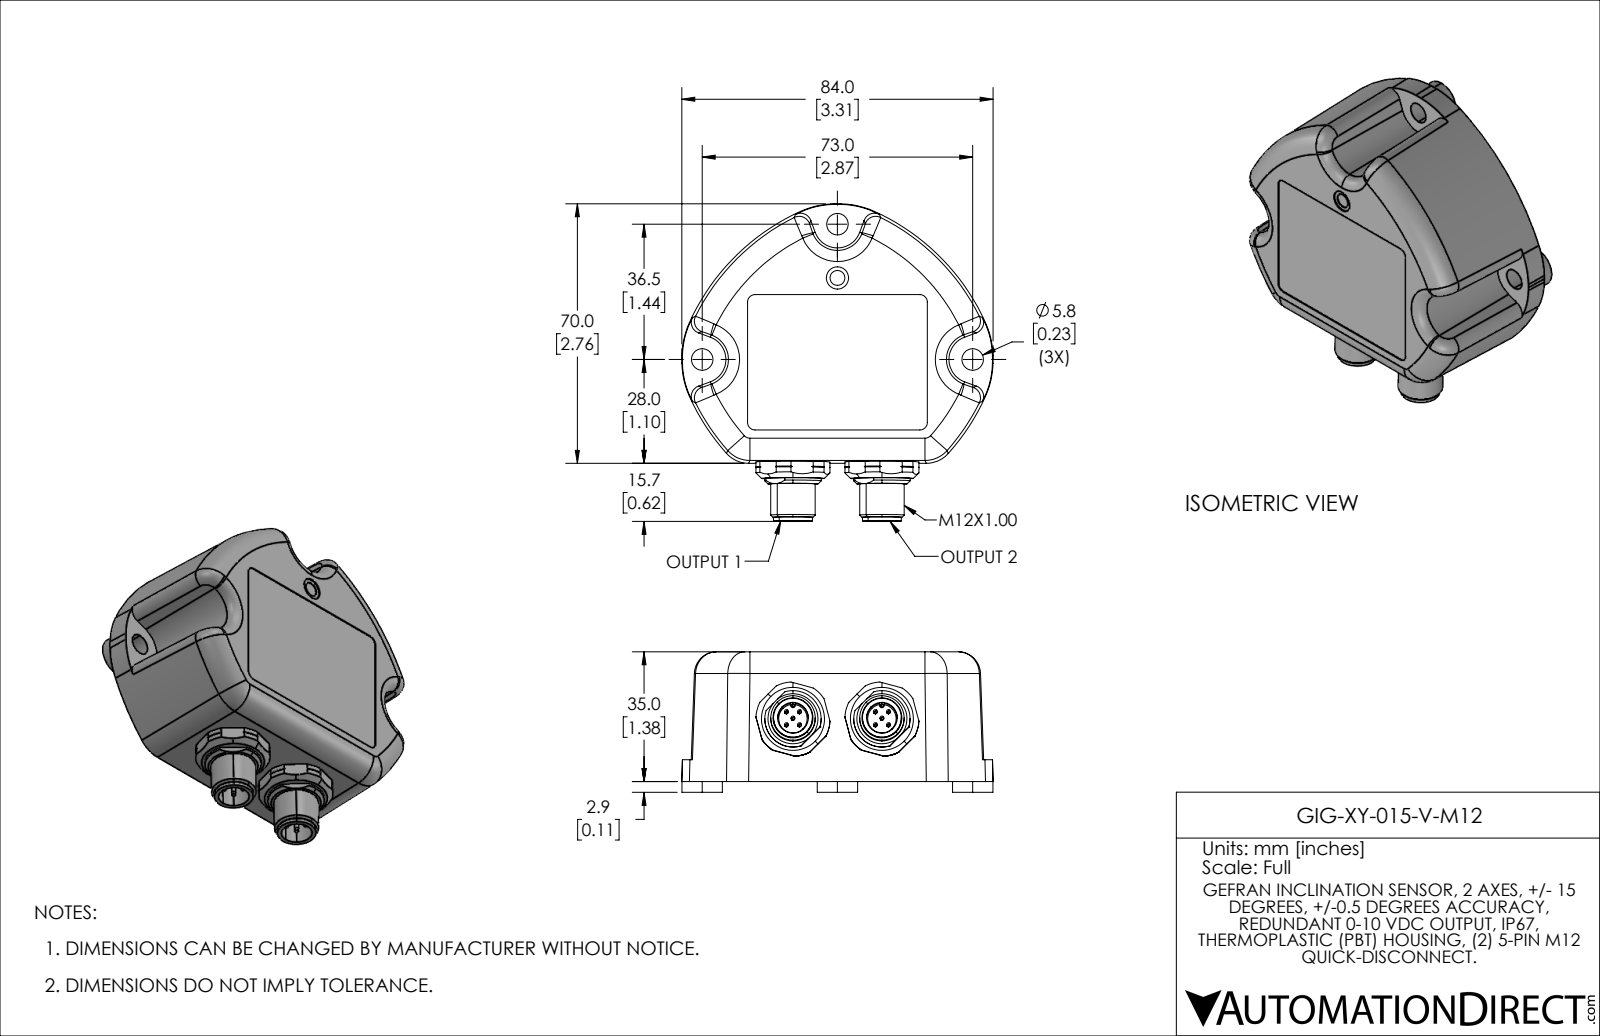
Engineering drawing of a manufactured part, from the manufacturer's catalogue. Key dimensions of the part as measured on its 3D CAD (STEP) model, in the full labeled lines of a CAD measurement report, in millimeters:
Part name (STEP PRODUCT): GIG-XY-015-V-M12
STEP written by: SolidWorks 2021 (AUTOMOTIVE_DESIGN)
Units: millimetres
Bodies: 1 solid, 365 faces (87 planar, 123 cylindrical, 155 other)
Overall size (bounding box): 85.7 × 84 × 37.9
Volume: 148 000 mm³ · Surface area: 20 890 mm²
Round holes (diameter × count): ⌀5.8 ×3, ⌀8.3 ×2, ⌀4 ×1, ⌀6 ×1
Round bosses / shafts (diameter × count): ⌀1 ×10, ⌀10.9 ×3, ⌀12 ×2, ⌀10.5 ×2
Partial cylindrical surfaces — rounded edges, fillets, slot ends (radius × count): R0.5 ×4, R2 ×4, R7.6 ×3, R0.6 ×2, R6.9 ×2, R10 ×2, R6 ×1, R7.6 ×1
Main face-to-face distances: 34.8, 35, 5.9, 28.9, 29.1, 2.9, 8.8, 37.7, 37.9, 17
Hole centre spacings: 42.6, 51.6, 14.5, 24, 73
